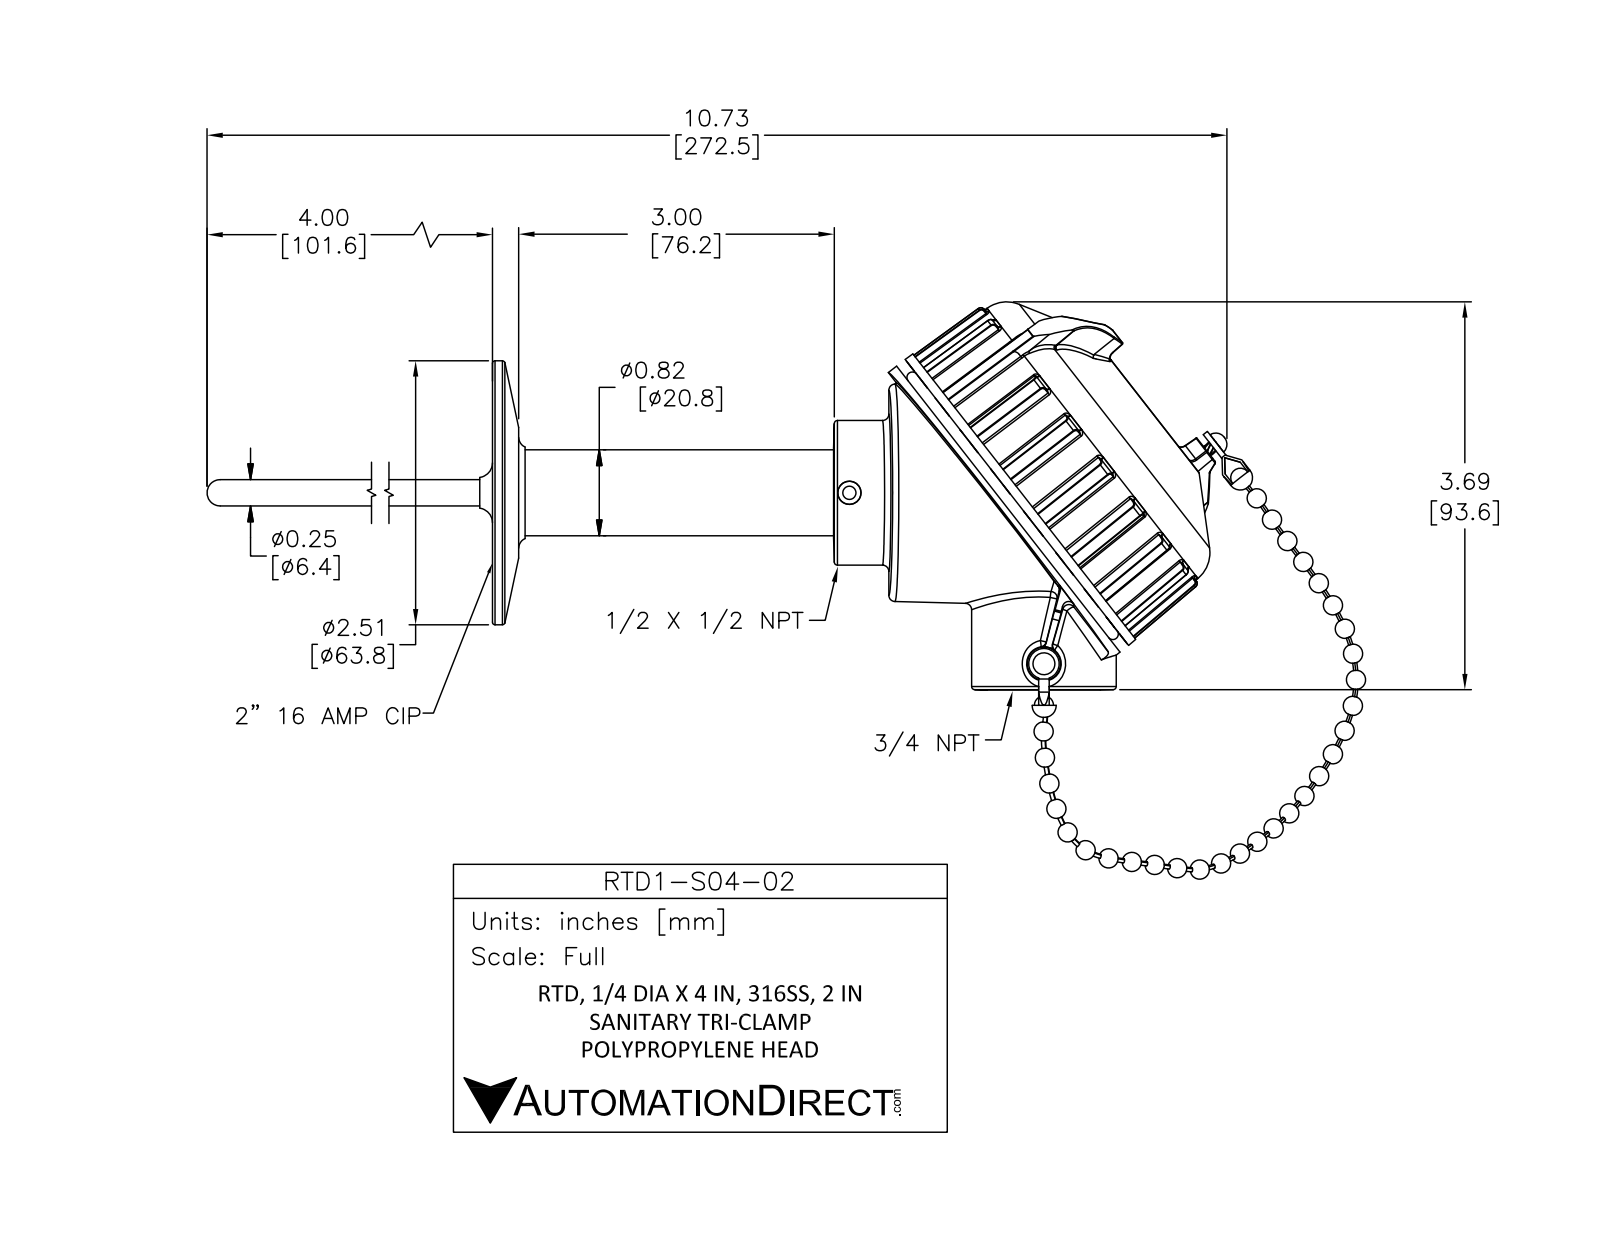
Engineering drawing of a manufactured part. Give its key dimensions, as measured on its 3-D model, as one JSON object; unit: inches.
{"part_name": "RTD1-S04-02", "step_written_by": "SolidWorks 2019 (CONFIG_CONTROL_DESIGN)", "units": "inches", "bodies": {"solids": 23, "faces": 1219, "planar": 155, "cylindrical": 209, "other": 855}, "overall_size": [10.903, 6.259, 3.45], "volume_in3": 27.74, "surface_area_in2": 116.7, "round_holes": [[0.075, 2], [0.104, 2], [0.128, 2], [0.125, 1], [0.175, 1], [0.175, 1], [0.622, 1], [3.339, 1]], "round_bosses_or_shafts": [[0.047, 44], [0.25, 3], [1.375, 2], [0.22, 2], [0.094, 2], [3.45, 1], [3.201, 1], [2.5, 1]], "partial_cylinders_radius": [[0.04, 18], [0.06, 6], [0.01, 4], [0.125, 3], [0.03, 2], [0.188, 2], [0.962, 2]], "face_to_face_distances": [5.875, 1.607, 5.625, 0.25, 1.603, 0.555, 3.875, 0.107, 0.103, 1.5], "hole_center_spacings": [0.299, 0.375, 0.65, 0.875, 1.512, 1.03, 1.199, 1.3]}
